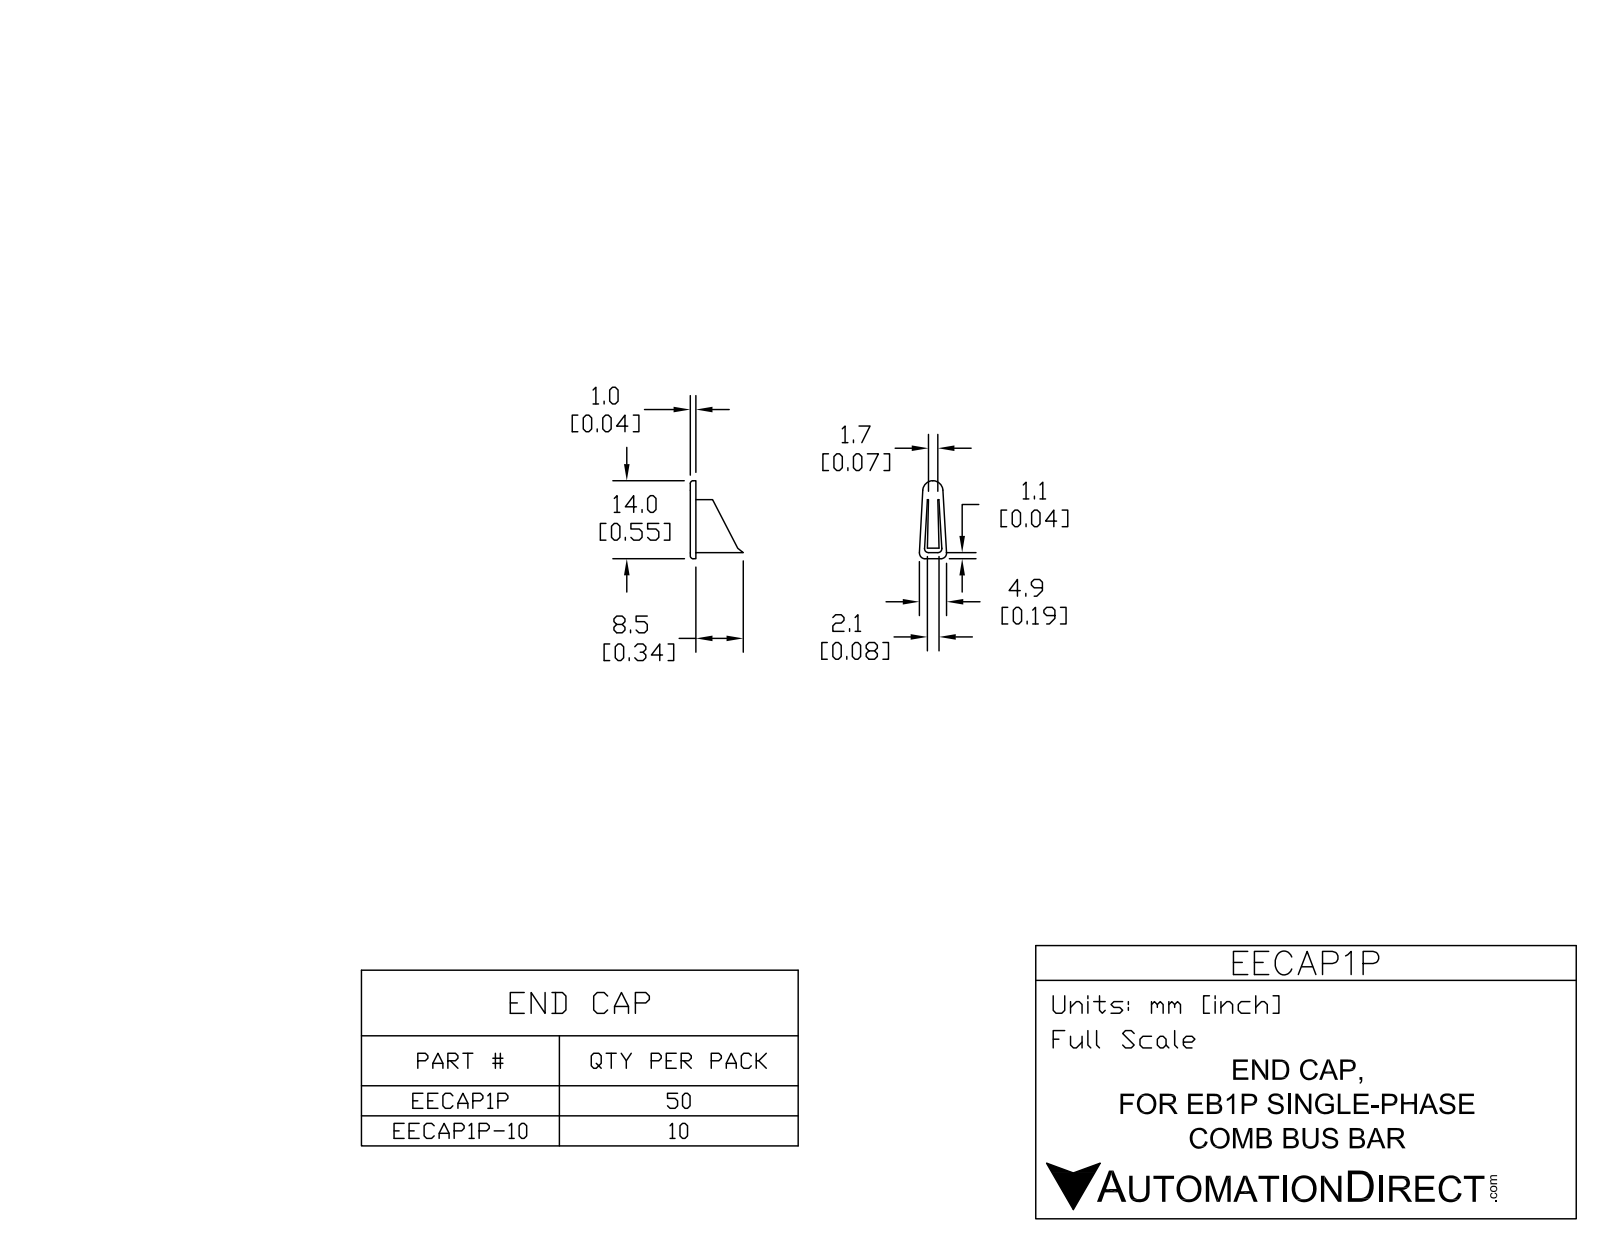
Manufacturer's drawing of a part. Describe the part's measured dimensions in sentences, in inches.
The part is named "EECAP1P". Its 3-D file was written by "SolidWorks 2011 (AUTOMOTIVE_DESIGN)". It is 1 solid with 28 faces: 14 planar, 10 cylindrical and 4 other. Overall it measures 0.56 by 0.362 by 0.19 inches. Its volume is 0.006 cubic inches and its surface area 0.588 square inches. Partial cylindrical surfaces (rounded edges, fillets, slot ends): 7 of radius 0.015, 1 of radius 0.07. The main face-to-face distances are 0.042, 0.345.
